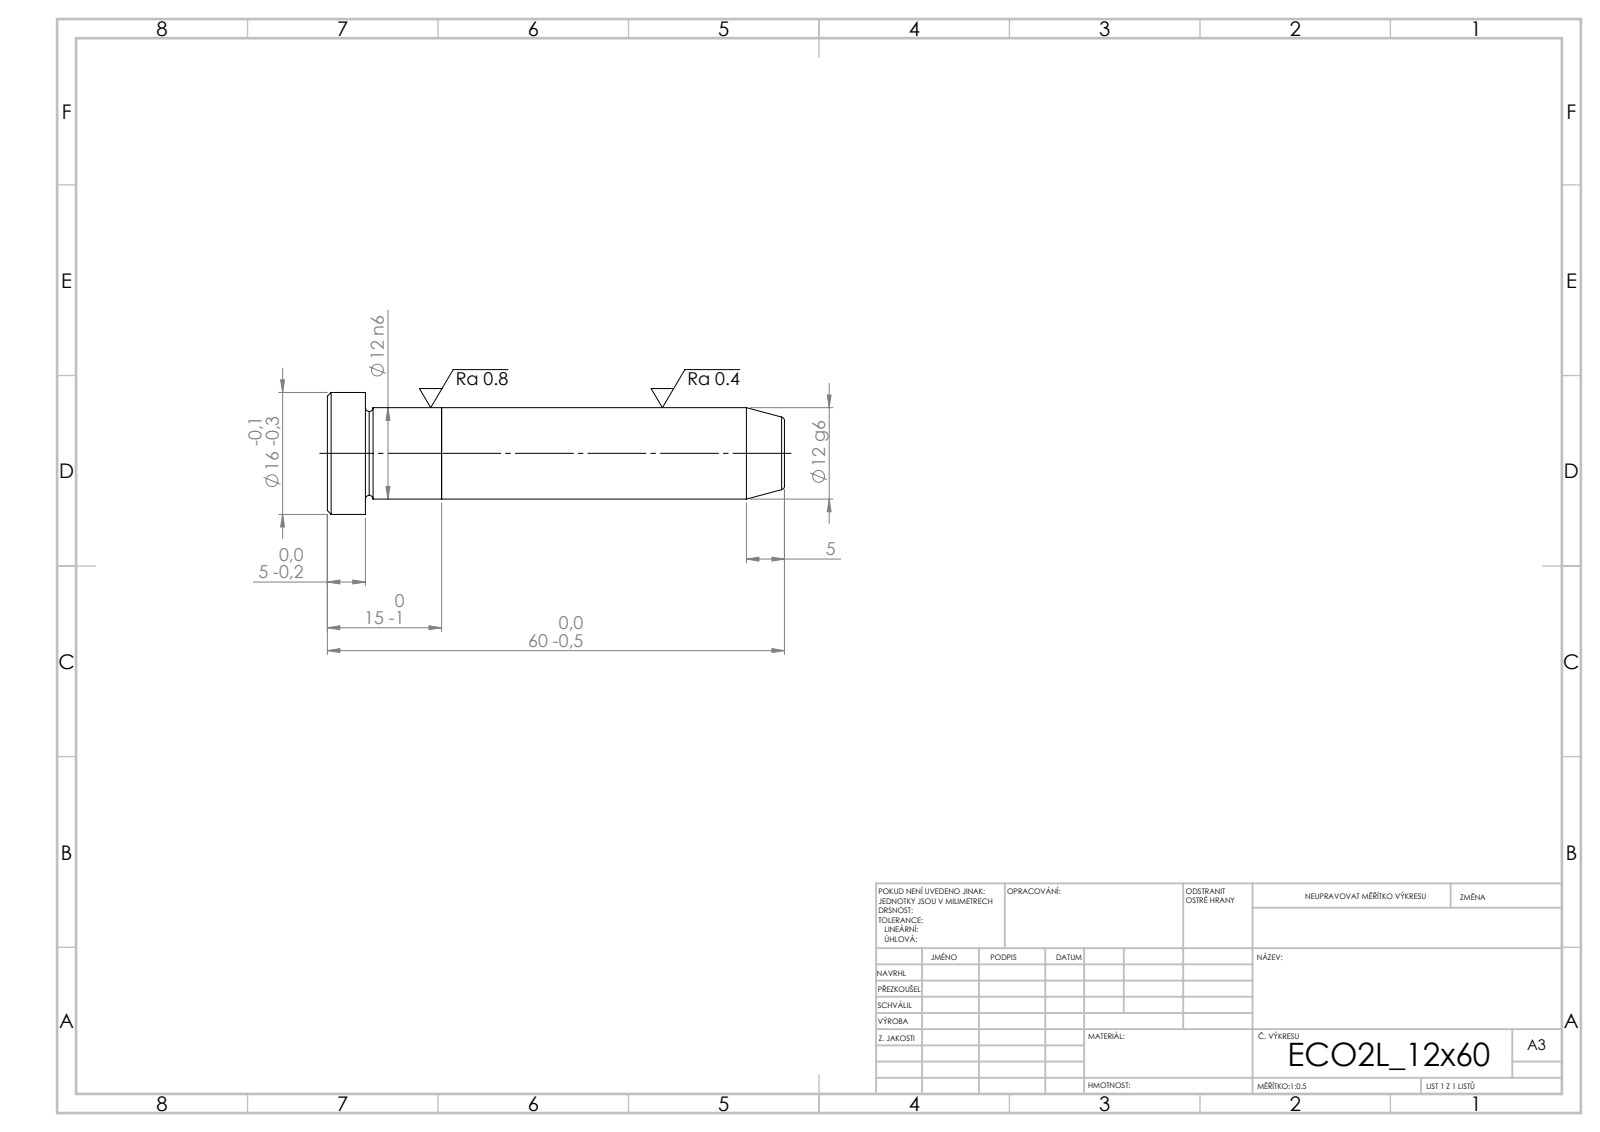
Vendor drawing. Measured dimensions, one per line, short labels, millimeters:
written by: SolidWorks 2019 (CONFIG_CONTROL_DESIGN)
unit: mm
bodies: 2 solids, 21 faces (5 planar, 6 cylindrical, 10 other)
size: 60 × 16 × 16
volume: 7 088 mm³; area: 2 893 mm²
bosses: 1× ⌀16, 1× ⌀12
face distances: 15, 10, 5, 45, 55, 60
